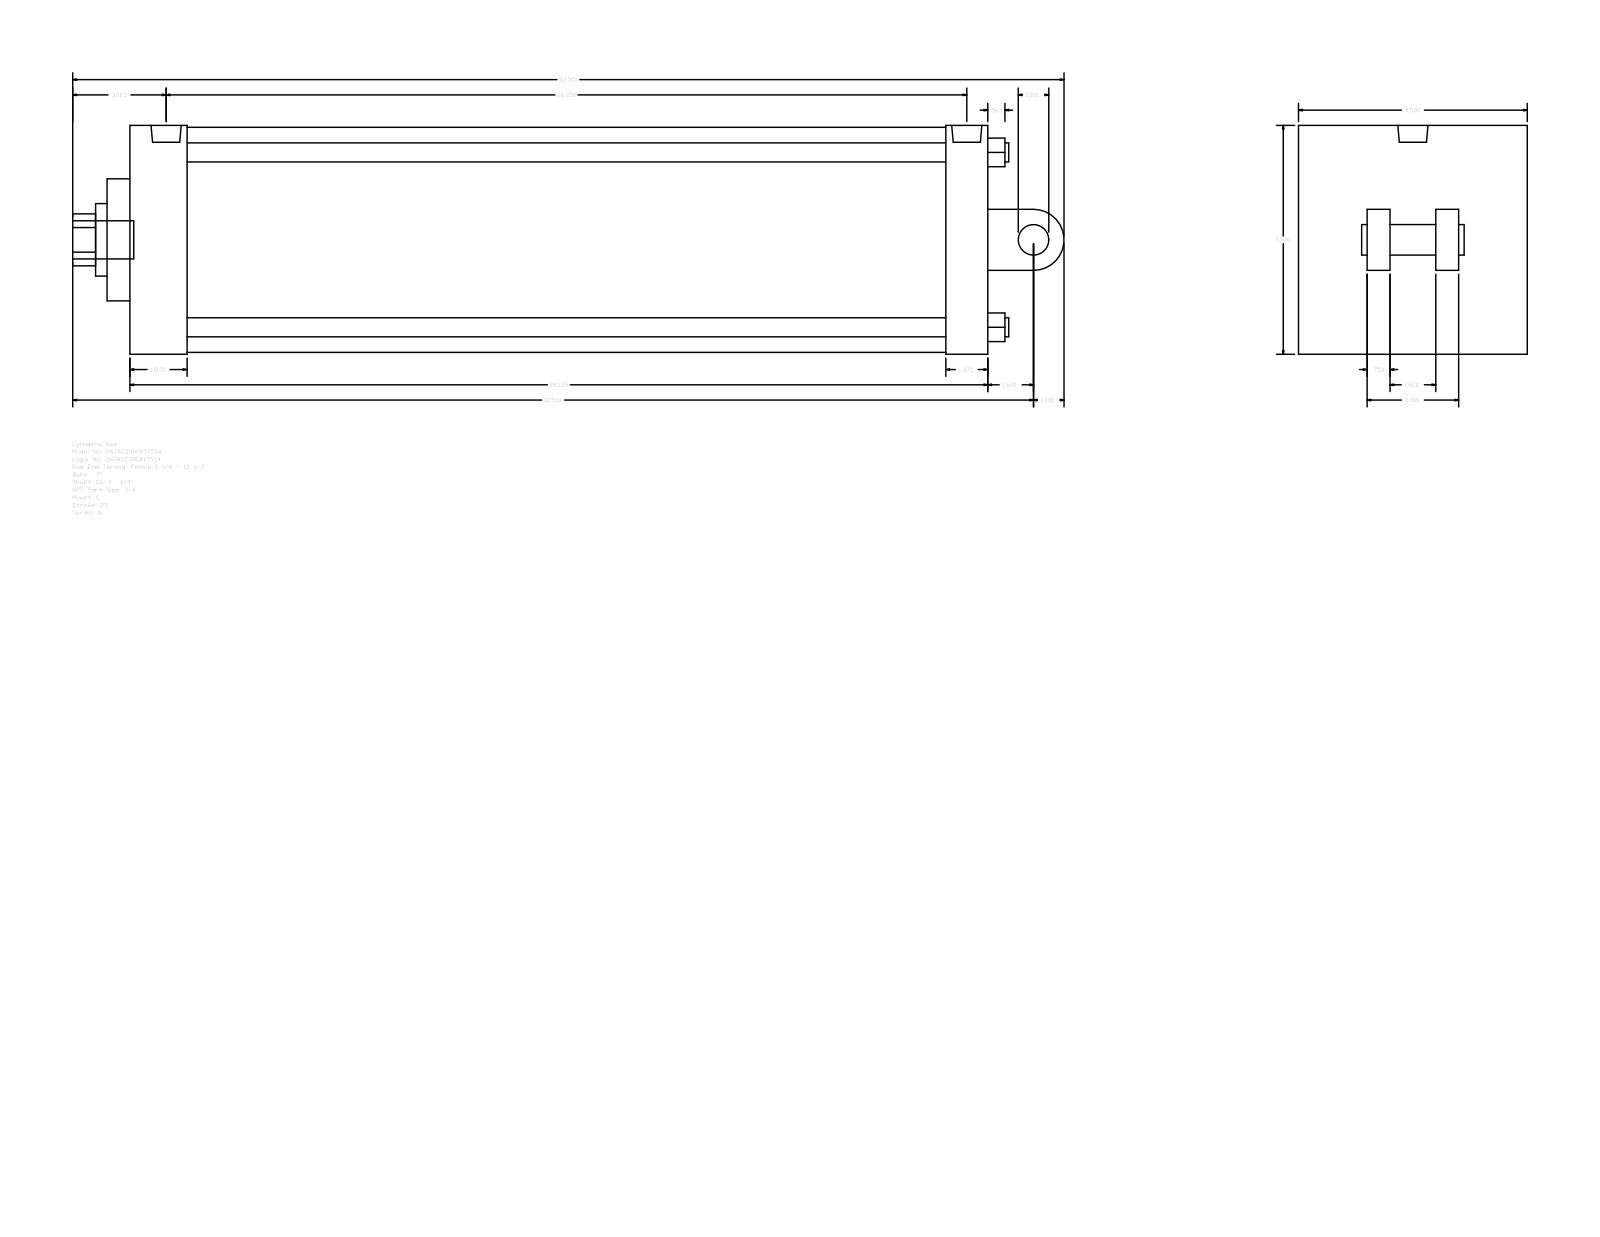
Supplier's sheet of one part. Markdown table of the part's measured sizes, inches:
| quantity | value |
| --- | --- |
| part name | A_C__0700_1.75 |
| STEP written by | GSSL Pune (CONFIG_CONTROL_DESIGN) |
| units | inches |
| bodies | 0 solids, 104 faces (75 planar, 29 cylindrical, 0 other) |
| overall size | 32.5 × 7.5 × 7.5 |
| round holes (diameter × count) | 0.625 × 4, 0.594 × 2, 0.989 × 1, 1.75 × 1, 2.375 × 1, 7.375 × 1 |
| round bosses / shafts (diameter × count) | 0.594 × 2, 1.25 × 1, 1 × 1, 0.989 × 1 |
| partial cylindrical surfaces (radius × count) | 0.852 × 1, 1 × 1 |
| main face-to-face distances | 7.5, 28.125, 0.75, 3, 2.25, 1.75, 1.375, 1.875, 26.25, 26.75 |
| hole center spacings | 4.052, 5.73, 8.103, 0.219 |
